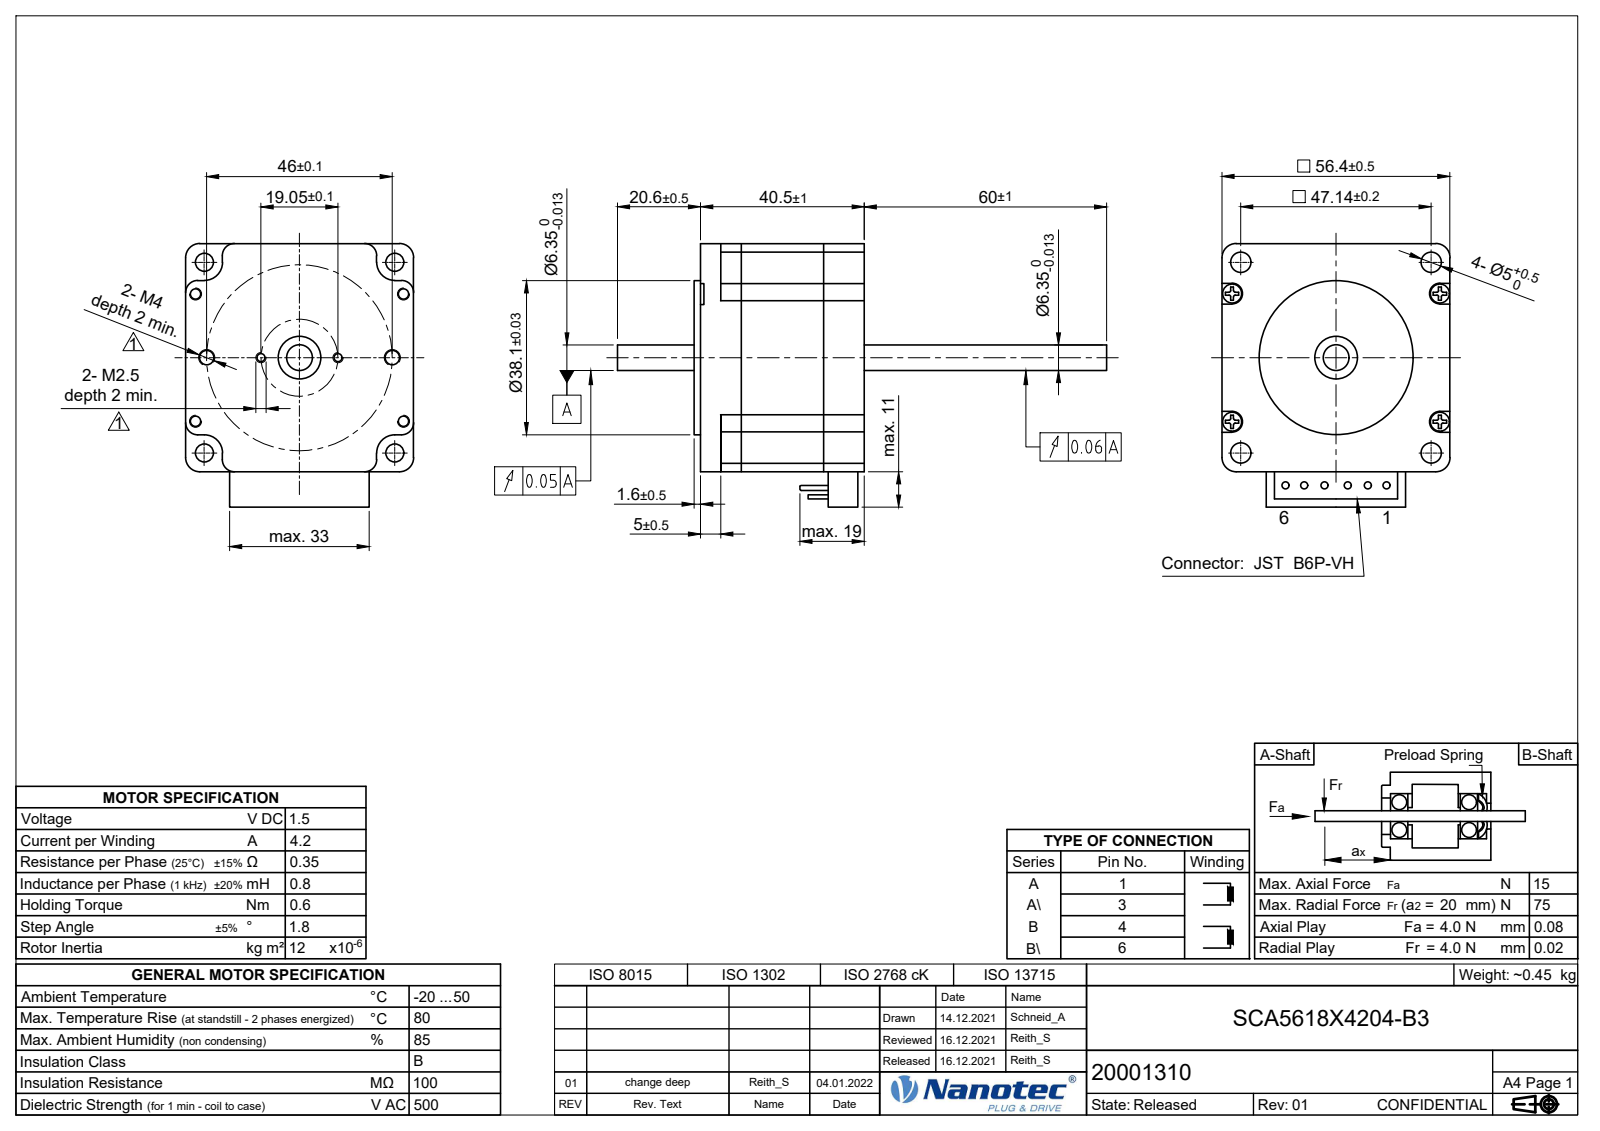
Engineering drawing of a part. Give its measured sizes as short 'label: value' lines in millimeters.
name: SCA5618X-B3_Shrinkwrap_1
written by: Autodesk Inventor 2019 (AUTOMOTIVE_DESIGN)
unit: mm
bodies: 4 solids, 178 faces (109 planar, 58 cylindrical, 11 other)
size: 121.1 × 66.9 × 56.54
volume: 124 302 mm³; area: 31 875 mm²
holes: 4× ⌀2.5, 4× ⌀3.2, 4× ⌀5, 2× ⌀2.01, 2× ⌀3.24, 1× ⌀2, 1× ⌀8.2, 1× ⌀10.5
bosses: 4× ⌀5.6, 1× ⌀38.1, 1× ⌀6.35
rounds: 12× R2.3, 8× R2, 4× R3.2, 4× R5
face distances: 24, 35.5, 11.5, 56.4, 5, 29, 40.5, 1.6, 6.6, 30.6
hole spacings: 7.94, 16.05, 22.49, 23.58, 27.43, 30, 33.33, 38.43
